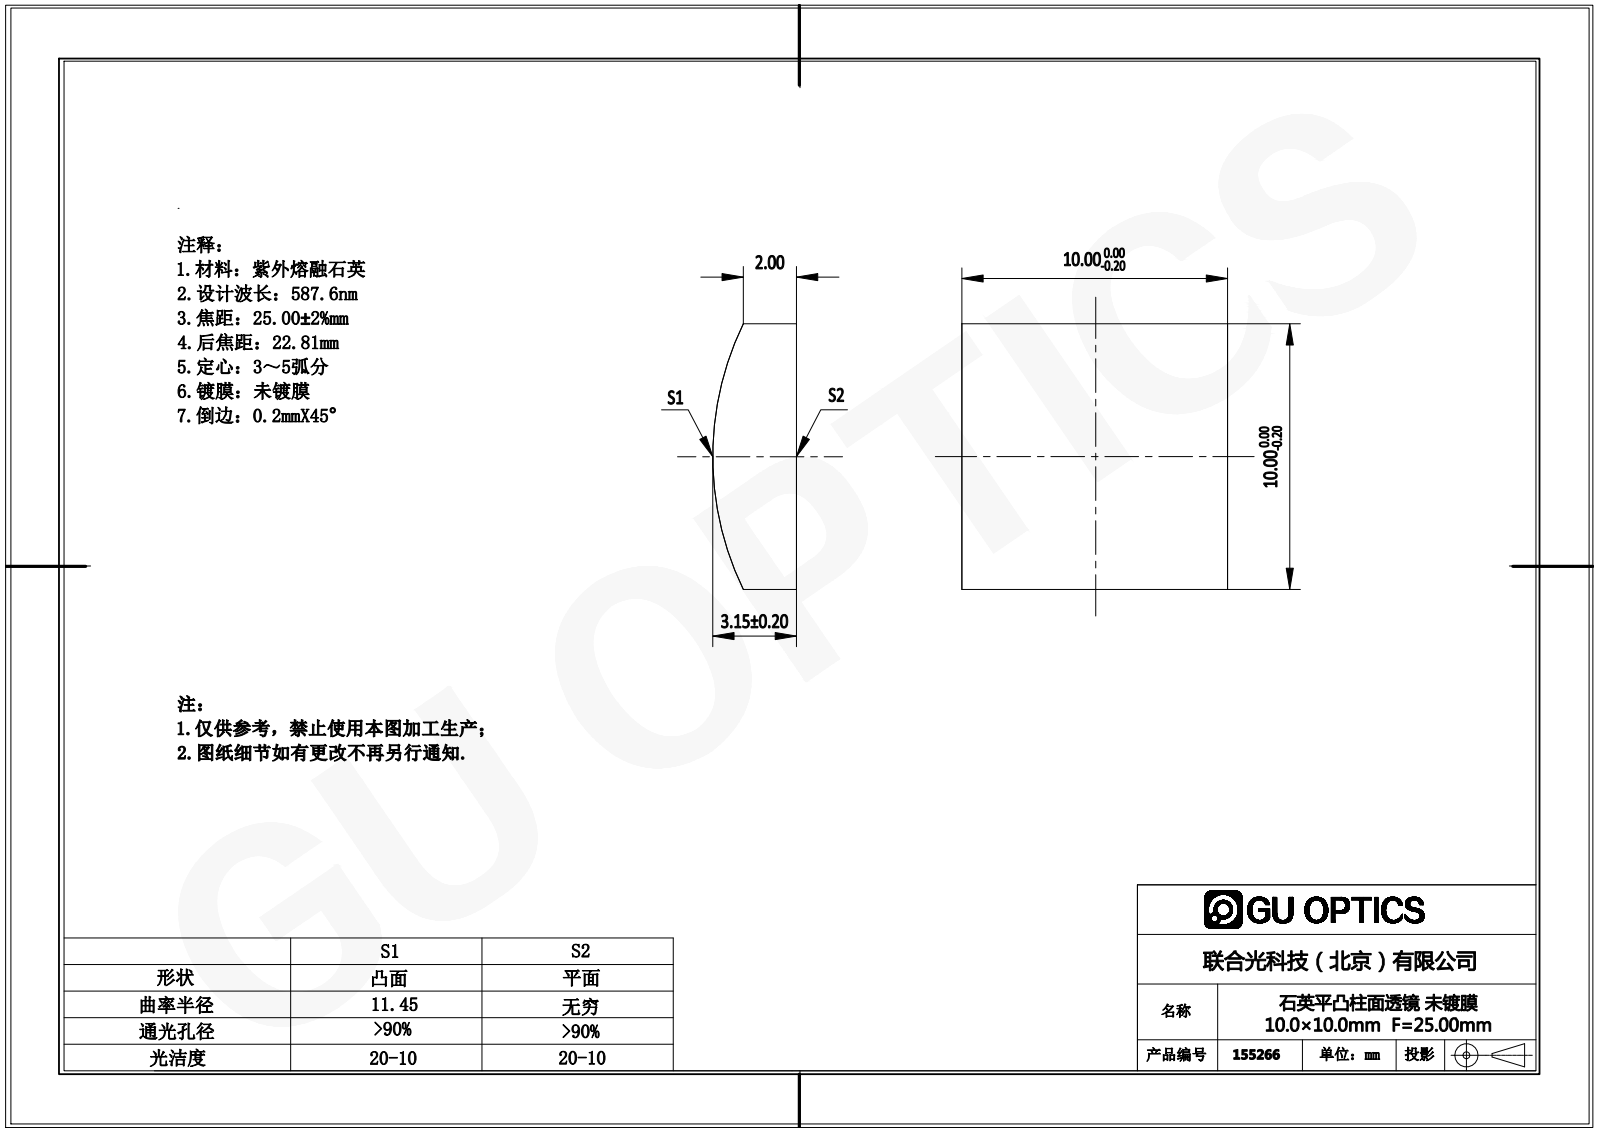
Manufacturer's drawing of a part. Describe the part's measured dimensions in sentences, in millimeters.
The part is named "155266". Its 3-D file was written by "SolidWorks 2016 (AUTOMOTIVE_DESIGN)". It is 1 solid with 6 faces: 5 planar, 1 cylindrical and 0 other. Overall it measures 10 by 10 by 3.15 millimeters. Its volume is 277 cubic millimeters and its surface area 299 square millimeters. Partial cylindrical surfaces (rounded edges, fillets, slot ends): 1 of radius 11.45. The main face-to-face distances are 10.
